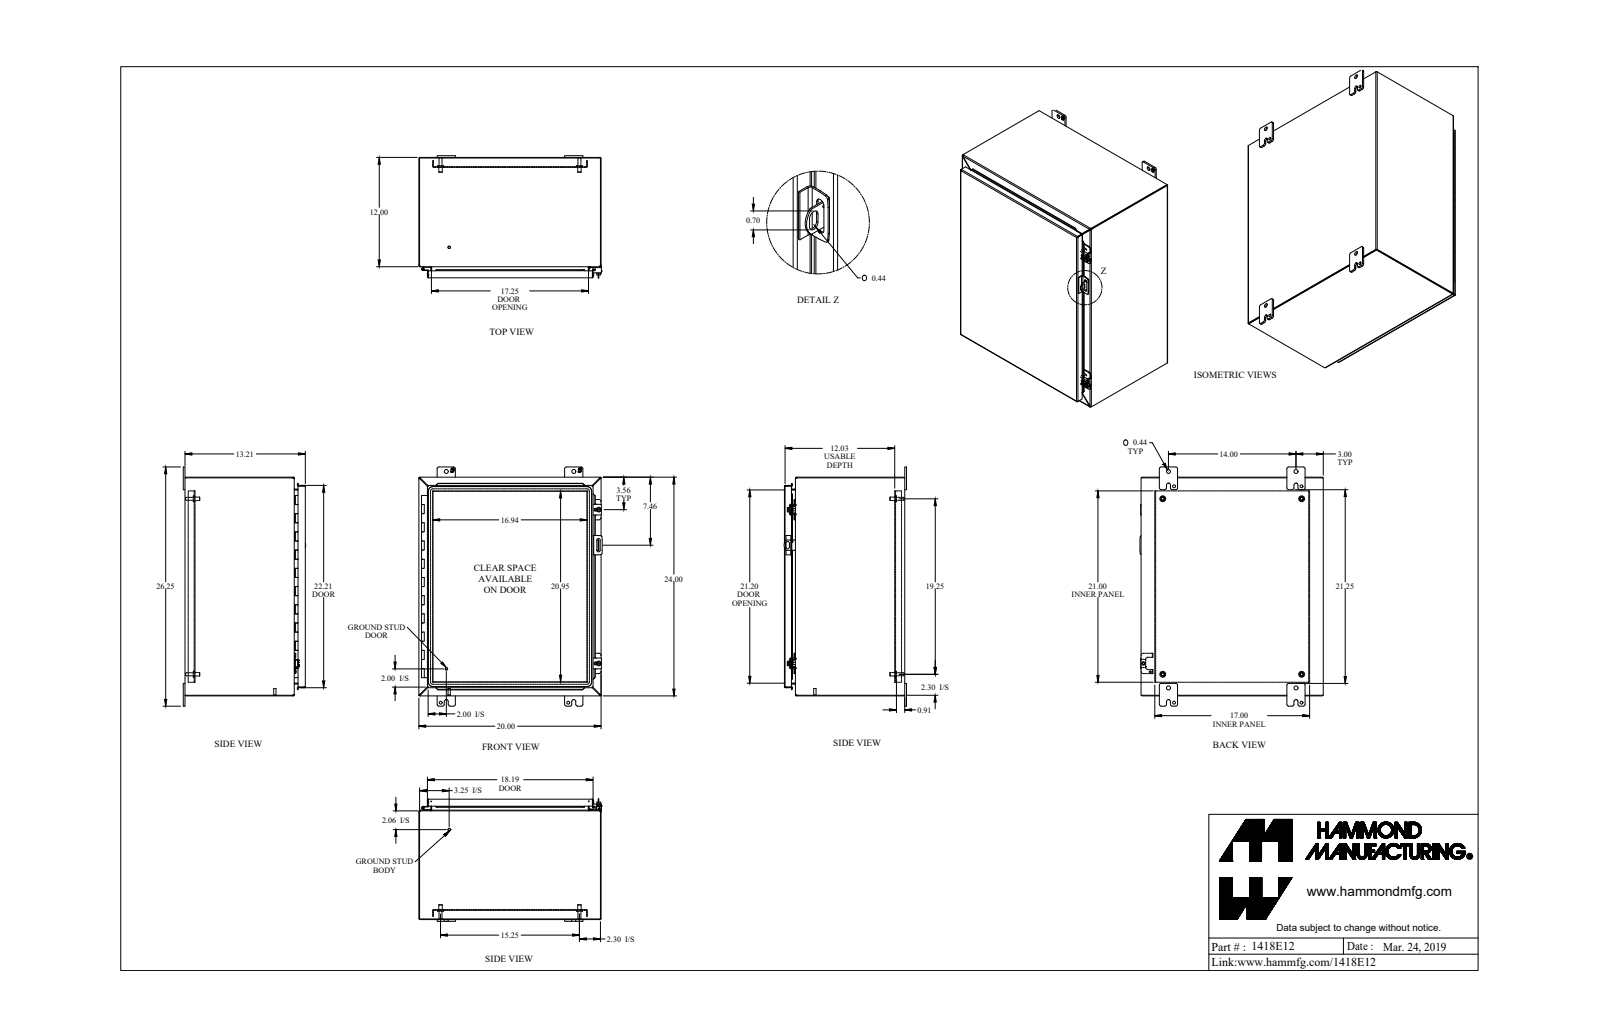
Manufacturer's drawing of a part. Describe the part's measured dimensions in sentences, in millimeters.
The part is named "1418E12". Its 3-D file was written by "SolidWorks 2019 (AUTOMOTIVE_DESIGN)". It is 28 solids with 930 faces: 624 planar, 258 cylindrical and 48 other. Overall it measures 666.8 by 510.4 by 341.3 millimeters. Its volume is 3 487 000 cubic millimeters and its surface area 3 603 000 square millimeters. Round holes: 4 of diameter 8, 4 of diameter 11.1, 4 of diameter 12.7, 2 of diameter 5.4, 1 of diameter 3.2, 1 of diameter 4.7. Round bosses or shafts: 4 of diameter 16.5, 4 of diameter 9.5, 4 of diameter 8.4, 2 of diameter 9.9, 2 of diameter 8, 2 of diameter 6.4, 1 of diameter 7.3. Partial cylindrical surfaces (rounded edges, fillets, slot ends): 25 of radius 1.2, 24 of radius 4.8, 20 of radius 6.4, 13 of radius 3.6, 12 of radius 3, 8 of radius 0.2, 8 of radius 1.1, 8 of radius 2. The main face-to-face distances are 1.8, 333.1, 506.2, 331.2, 607.8, 334.9, 2.4, 309.3, 307.4, 23.8. The hole center spacings are 355.6, 44.1, 603.3, 700.3, 61.8, 77.9, 373.4, 387.4.
